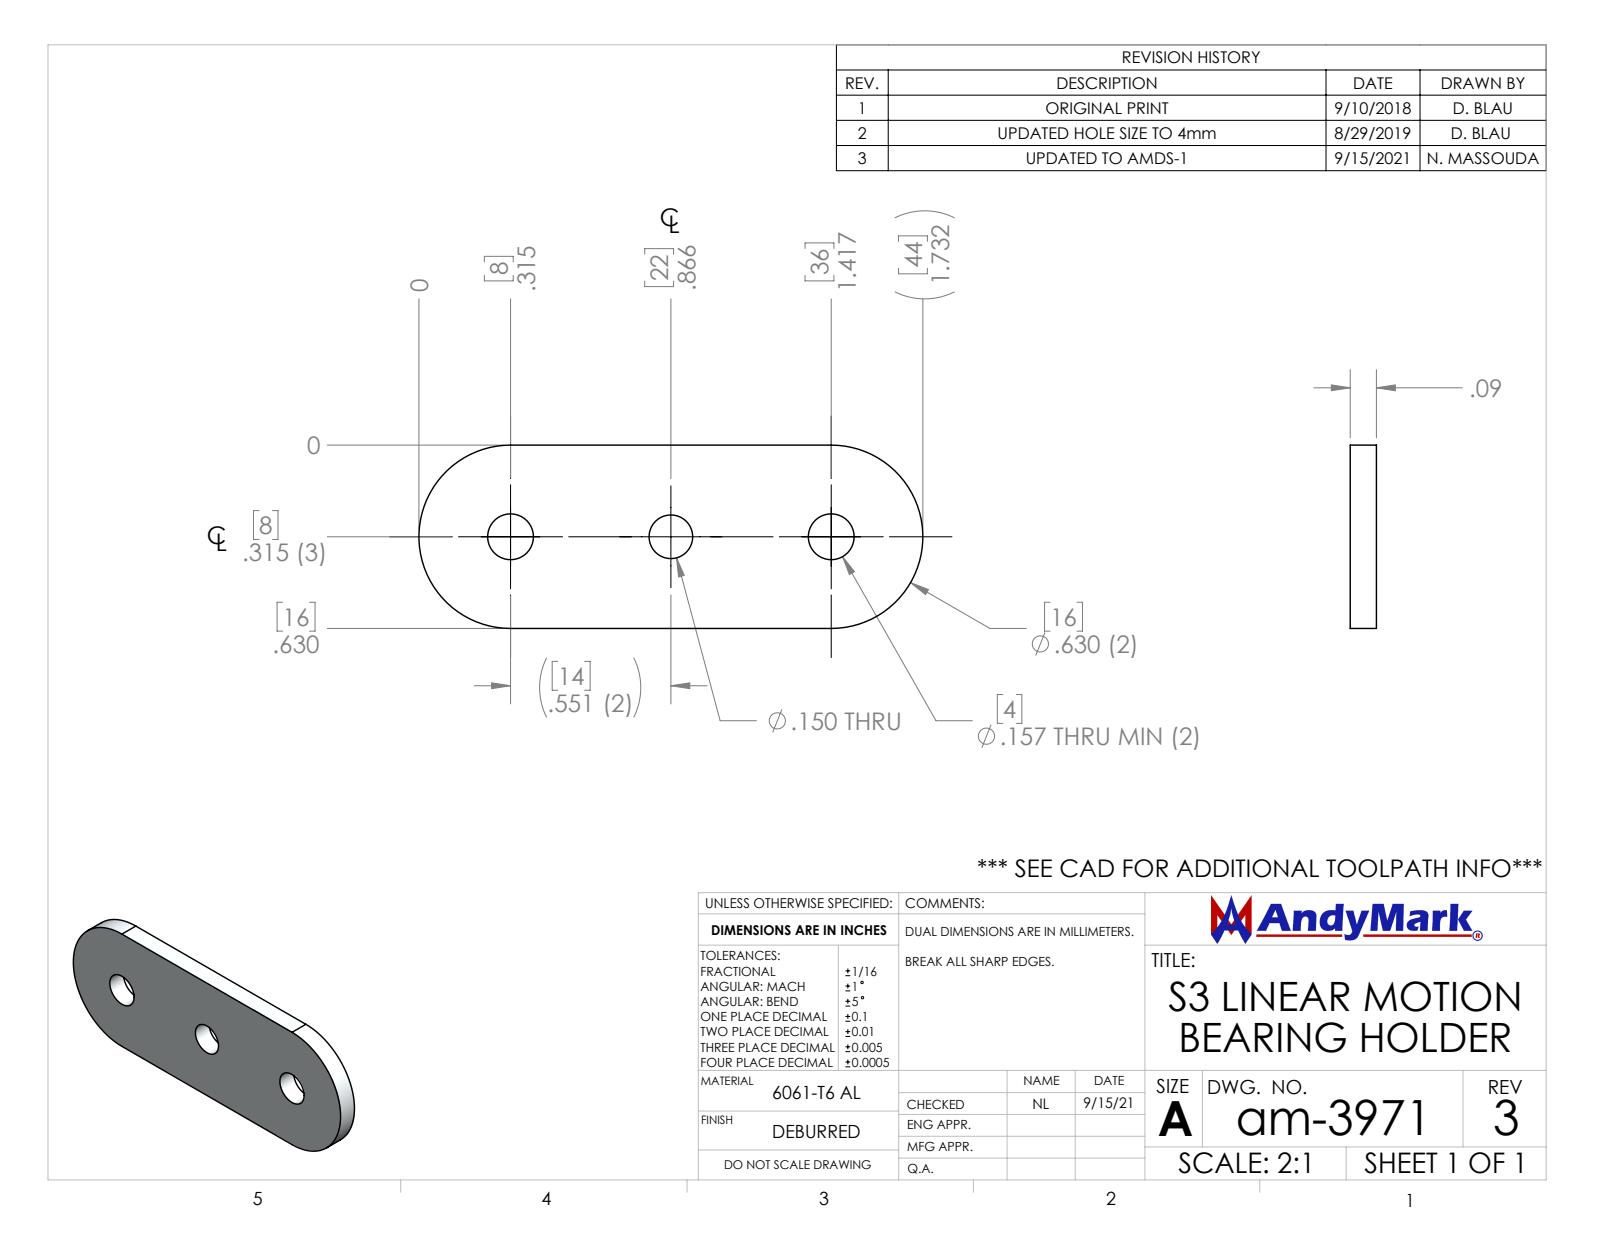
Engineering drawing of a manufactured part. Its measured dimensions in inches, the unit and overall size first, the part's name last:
Units: inches
Overall size (bounding box): 1.732 × 0.63 × 0.09
Round holes (diameter × count): ⌀0.157 ×2, ⌀0.15 ×1
Partial cylindrical surfaces — rounded edges, fillets, slot ends (radius × count): R0.315 ×2
Main face-to-face distances: 0.09, 0.63
Hole centre spacings: 0.551, 1.102
Volume: 0.085 in³ · Surface area: 2.407 in²
Bodies: 1 solid, 13 faces (4 planar, 9 cylindrical, 0 other)
Part name (STEP PRODUCT): am-3971 S3 Linear Motion Bearing Holder
STEP written by: SolidWorks 2021 (CONFIG_CONTROL_DESIGN)
